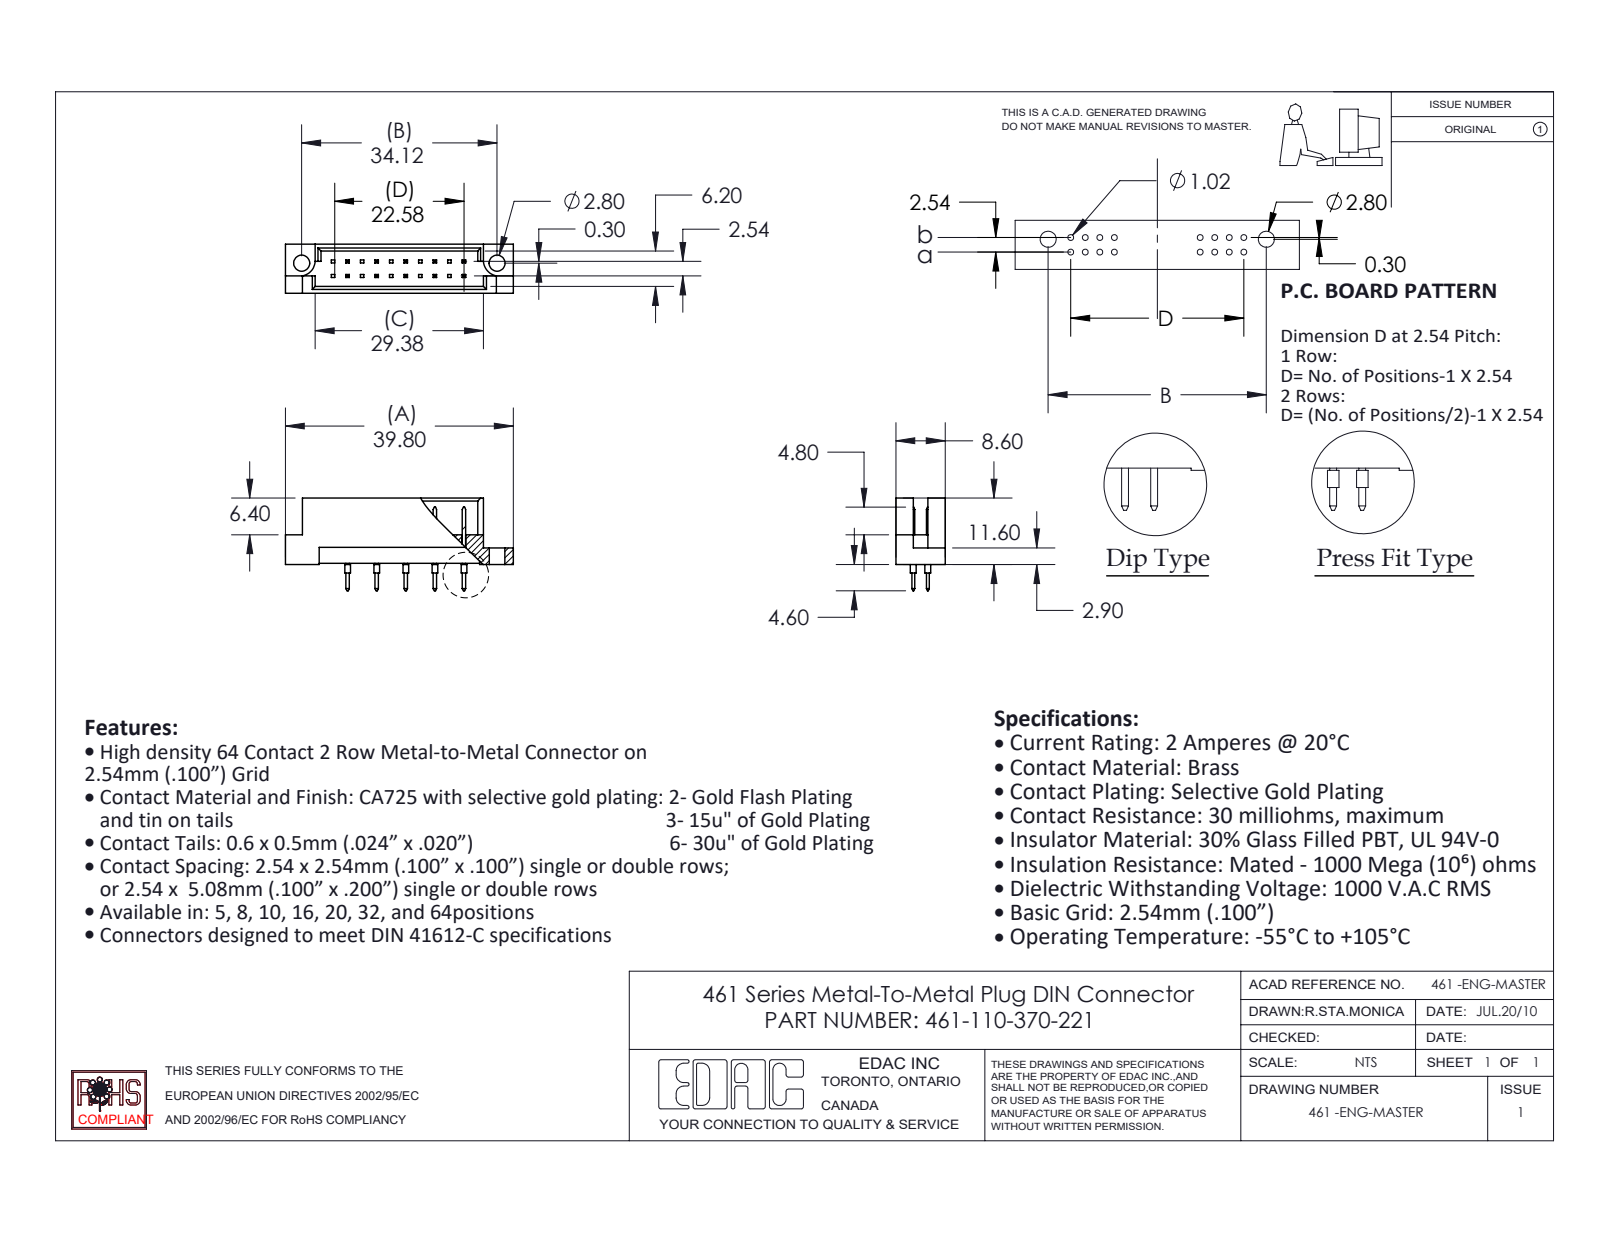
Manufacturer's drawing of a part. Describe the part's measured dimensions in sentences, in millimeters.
The part is named "461-290_70; 461 Part_20; 461-110-370-221". Its 3-D file was written by "SolidWorks 2020 (CONFIG_CONTROL_DESIGN)". It is 11 solids with 348 faces: 322 planar, 26 cylindrical and 0 other. Overall it measures 39.8 by 16.2 by 8.6 millimeters. Its volume is 1 955 cubic millimeters and its surface area 2 679 square millimeters. Round holes: 2 of diameter 2.8. Round bosses or shafts: 10 of diameter 1. Partial cylindrical surfaces (rounded edges, fillets, slot ends): 2 of radius 2.8. The main face-to-face distances are 1.2, 7.4, 8.6, 6.2, 5, 2.54, 5.08, 1.58, 2.78, 3.28. The hole center spacings are 34.12.
